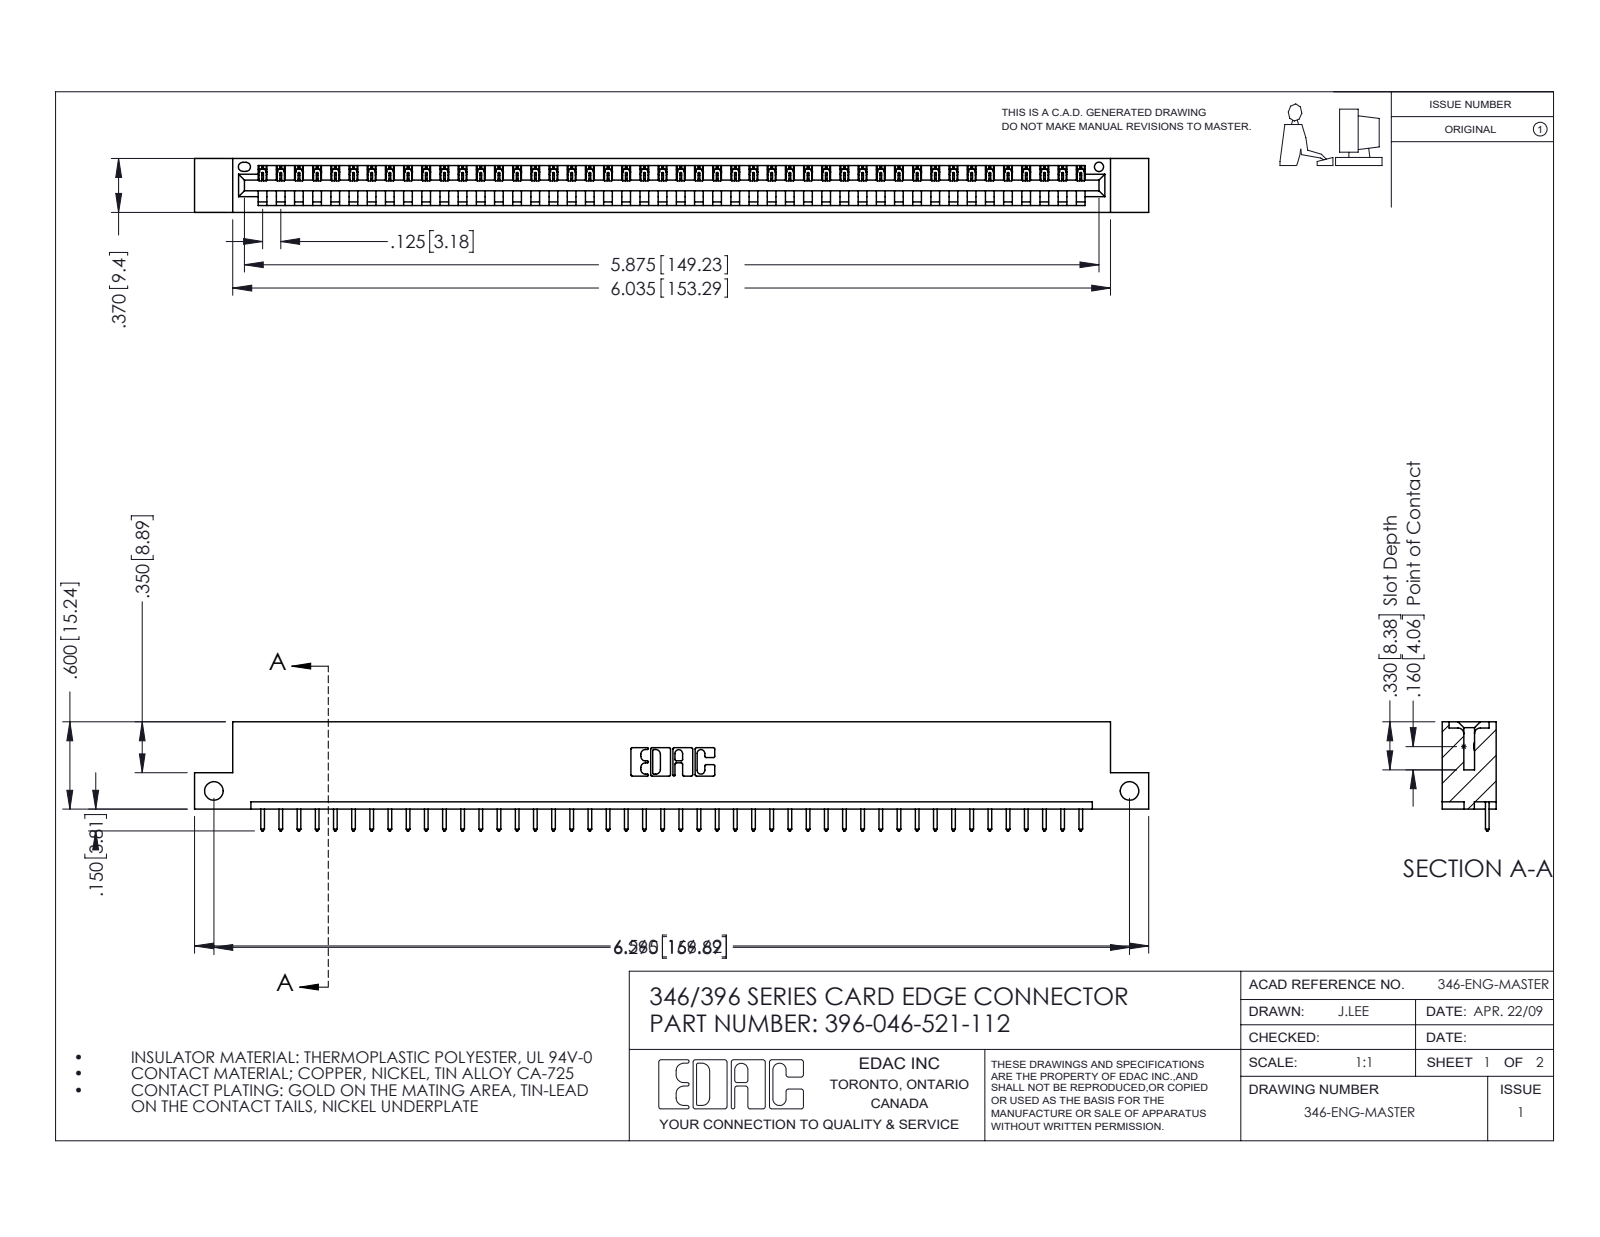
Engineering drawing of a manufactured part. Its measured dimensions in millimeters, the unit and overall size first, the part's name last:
Units: millimetres
Overall size (bounding box): 166.6 × 19.1 × 9.4
Round holes (diameter × count): ⌀3.3 ×2, ⌀1.6 ×1
Partial cylindrical surfaces — rounded edges, fillets, slot ends (radius × count): R0.2 ×92, R0.3 ×92, R0.3 ×22, R0.2 ×6, R0.8 ×6, R0.7 ×3, R0.8 ×2, R1 ×2
Main face-to-face distances: 1.2, 8.2, 9.4, 6.4, 1.8, 7.6, 0.6, 3.8, 5.6, 2.5
Hole centre spacings: 159.9
Volume: 15 800 mm³ · Surface area: 19 070 mm²
Bodies: 47 solids, 2790 faces (1916 planar, 874 cylindrical, 0 other)
Part name (STEP PRODUCT): 396-046-521-112; 345-292-001_345-293-121; 346 Part_Flush Mounting Lugs - Side Mount
STEP written by: SolidWorks 2016 (CONFIG_CONTROL_DESIGN)
